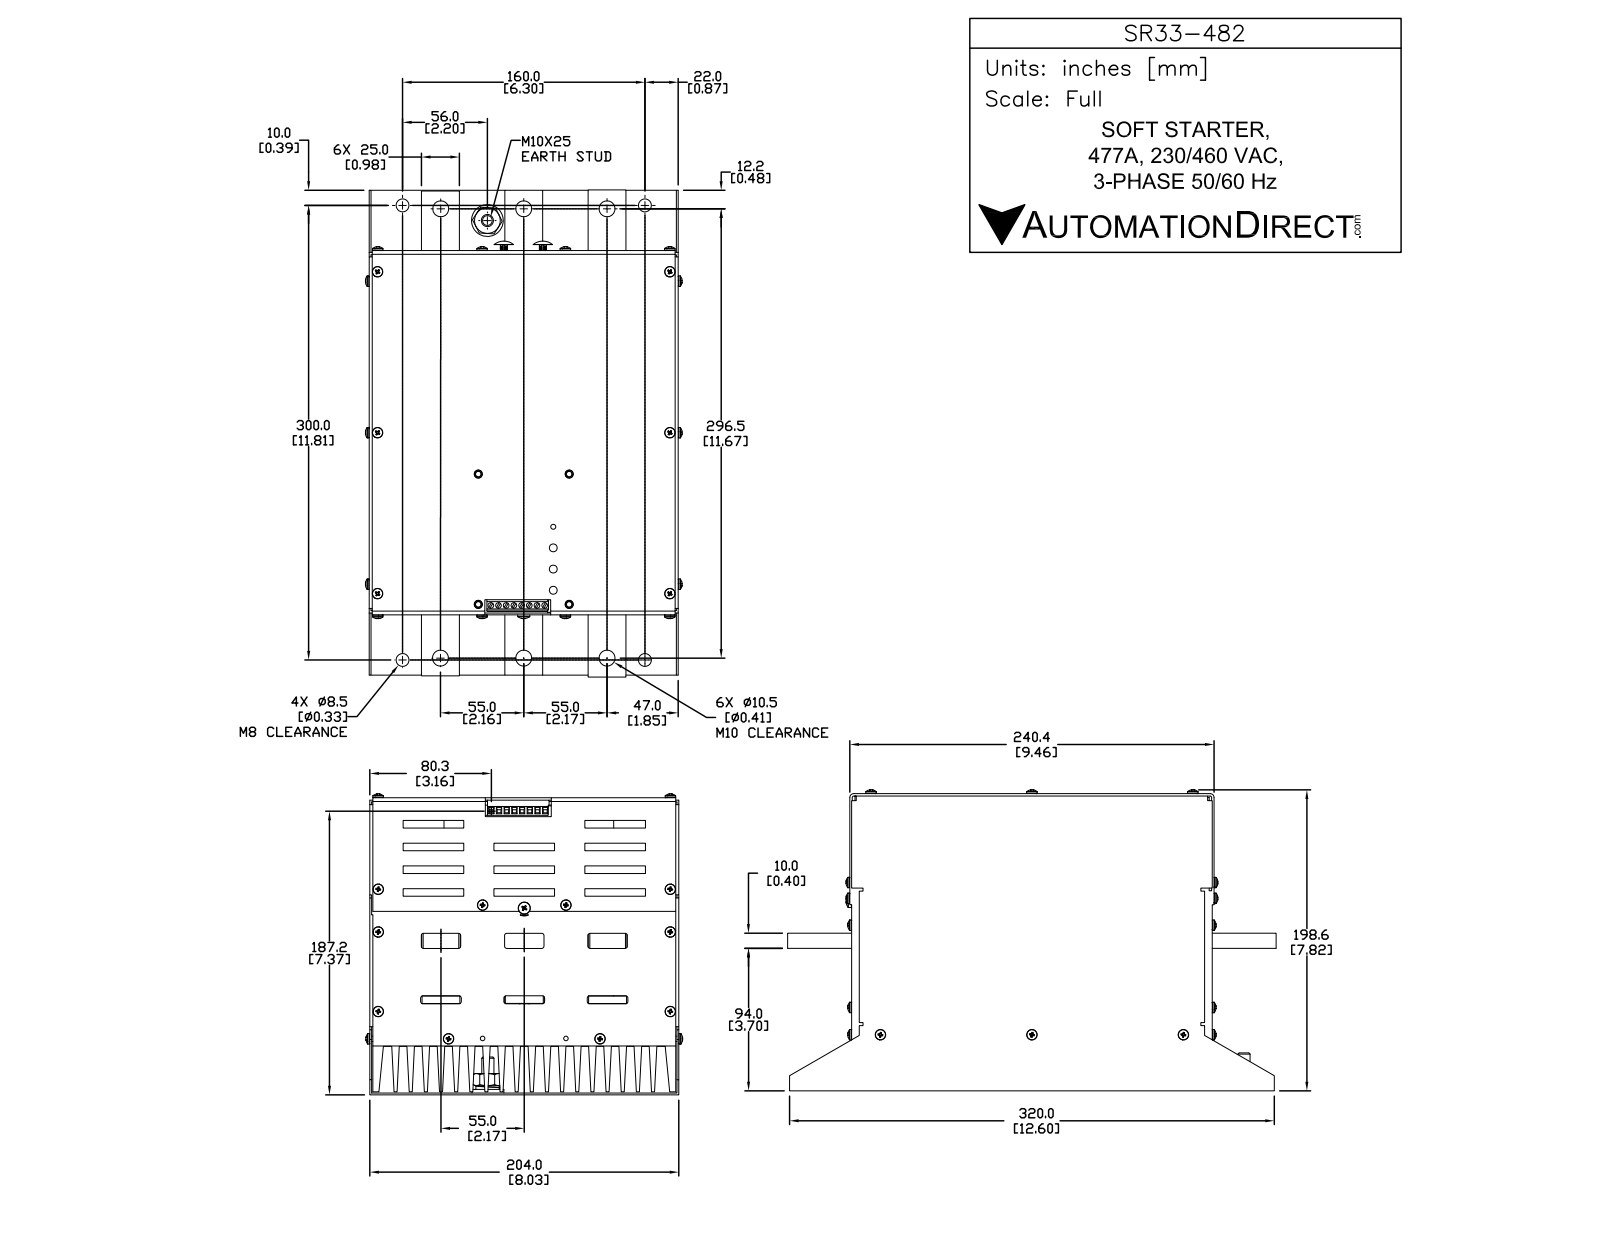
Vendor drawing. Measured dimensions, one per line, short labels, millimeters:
name: SR33-482
written by: SolidWorks 2013 (AUTOMOTIVE_DESIGN)
unit: mm
bodies: 2 solids, 1114 faces (755 planar, 153 cylindrical, 206 other)
size: 322.8 × 203 × 199.1
volume: 7 932 000 mm³; area: 999 241 mm²
holes: 8× ⌀3.82, 4× ⌀8.5
bosses: 14× ⌀6.9, 7× ⌀16, 7× ⌀8
rounds: 14× R2, 8× R1
face distances: 9.99, 19.98, 29.97, 39.96, 49.95, 59.94, 15, 69.93, 79.92, 89.91
hole spacings: 4.92, 9.84, 14.76, 19.68, 24.6, 29.52, 160, 300
